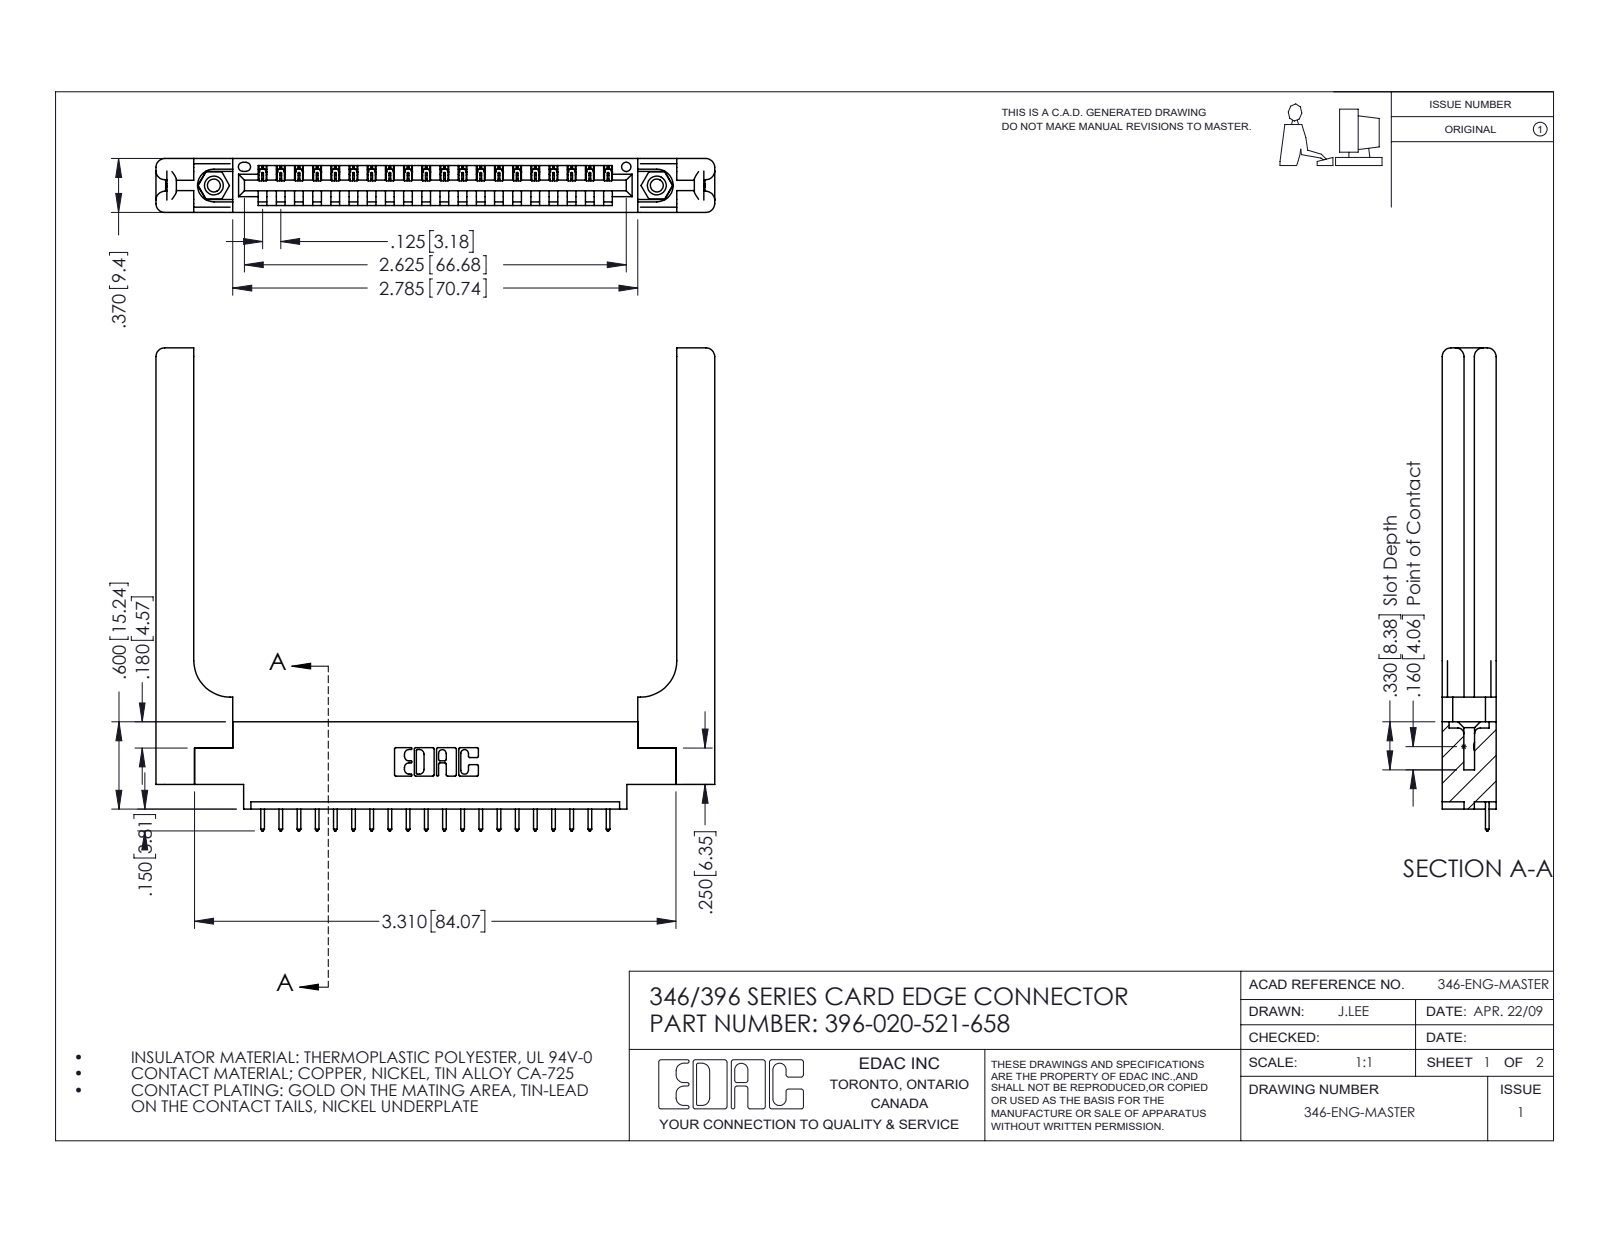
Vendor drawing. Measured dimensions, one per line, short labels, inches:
name: 346-220-058_345-220-058; 346 Part_0.170 Offset - 0.156 Dia-TH; 396-020-521-658; 345-292-001_345-293-121 (+1 more)
written by: SolidWorks 2016 (CONFIG_CONTROL_DESIGN)
unit: in
bodies: 25 solids, 1542 faces (1028 planar, 454 cylindrical, 60 other)
size: 3.841 × 3.32 × 0.37
volume: 1.007 in³; area: 24.93 in²
holes: 2× ⌀0.089, 2× ⌀0.125, 2× ⌀0.156, 1× ⌀0.064
bosses: 2× ⌀0.155
rounds: 40× R0.006, 40× R0.01, 22× R0.01, 16× R0.06, 6× R0.007, 6× R0.031, 3× R0.026, 2× R0.03
face distances: 0.37, 0.072, 0.15, 0.148, 0.048, 0.322, 0.25, 0.102, 0.22, 0.173
hole spacings: 0.246, 2.837, 3.045
